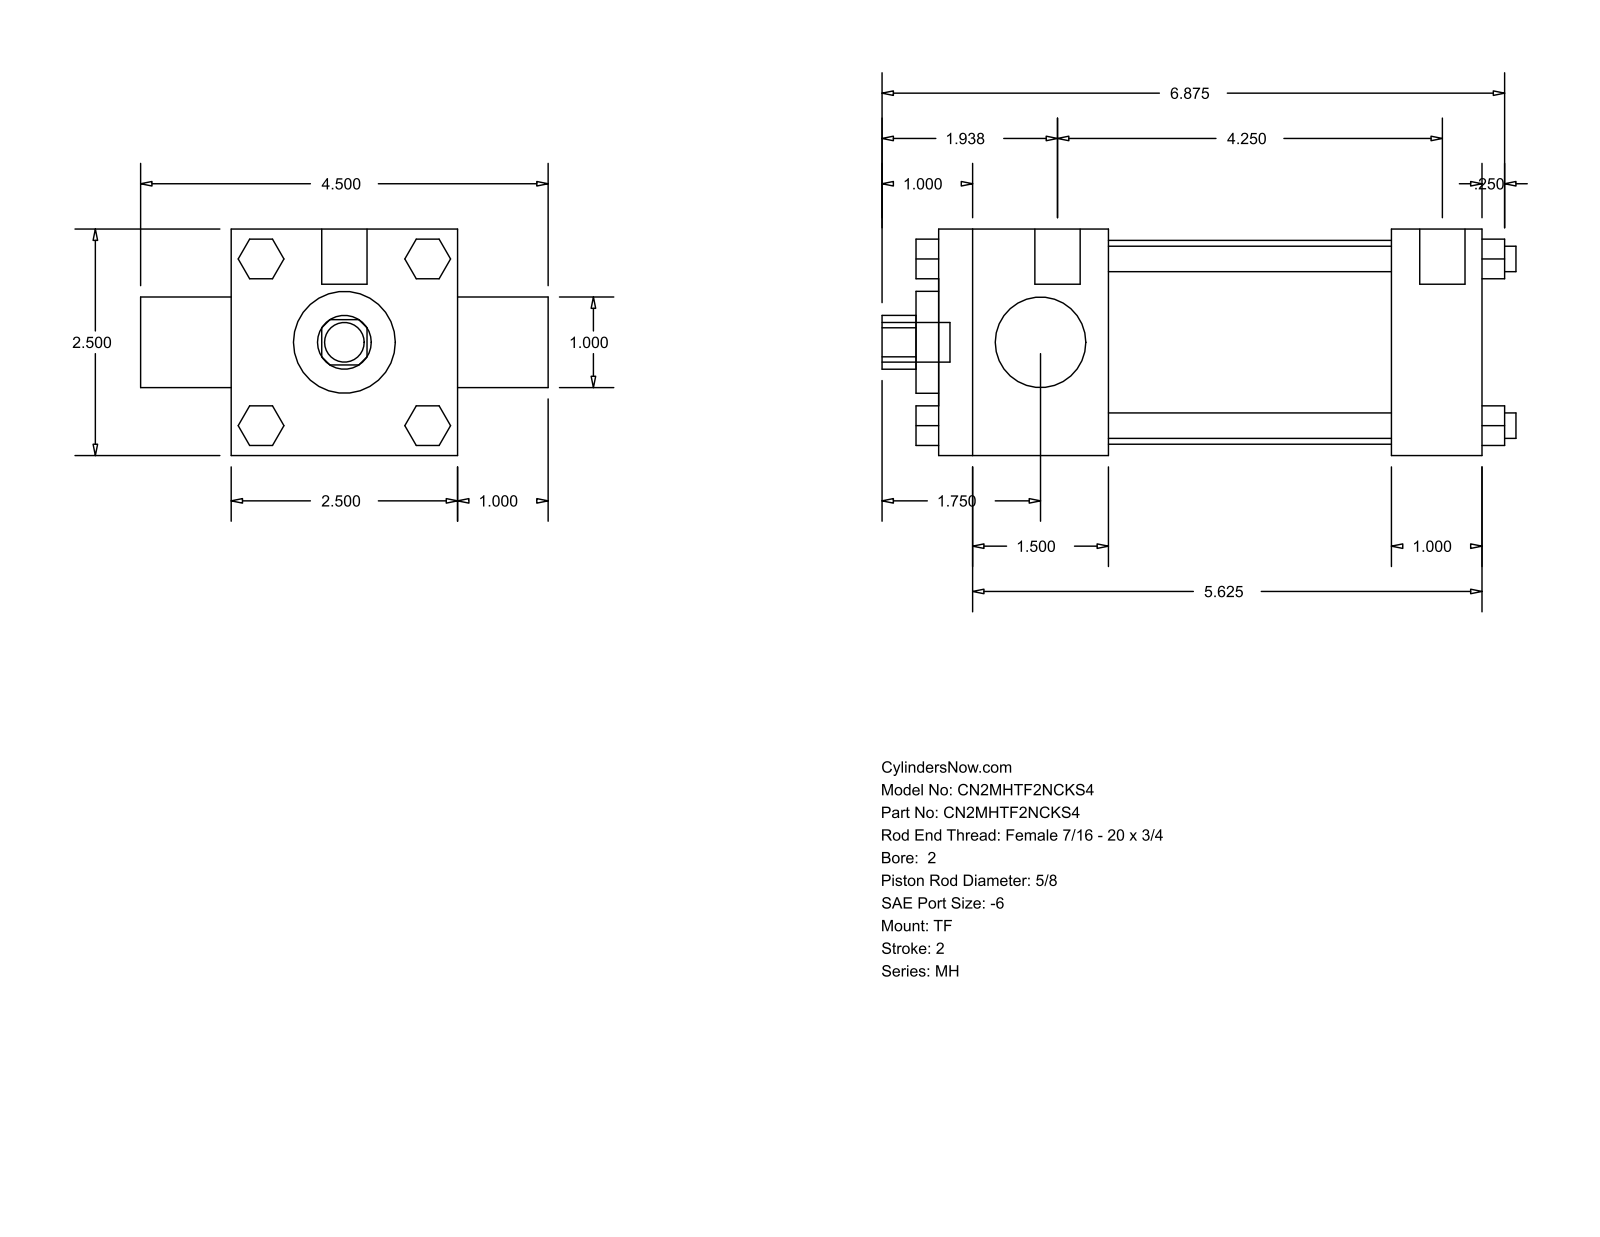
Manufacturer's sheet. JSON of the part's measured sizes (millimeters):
{"part_name": "MH_TF__0200_0.625", "step_written_by": "GSSL Pune (CONFIG_CONTROL_DESIGN)", "units": "millimeters", "bodies": {"solids": 0, "faces": 120, "planar": 92, "cylindrical": 28, "other": 0}, "overall_size": [177.8, 114.3, 63.5], "round_holes": [[15.88, 1], [25.4, 1], [28.57, 1], [57.15, 1]], "round_bosses_or_shafts": [[7.14, 4], [5.56, 3], [12.7, 2], [11.11, 1]], "partial_cylinders_radius": [[7.54, 1]], "face_to_face_distances": [63.5, 152.4, 25.4, 47.62, 127, 79.38, 104.78, 88.9, 158.75, 6.35]}
